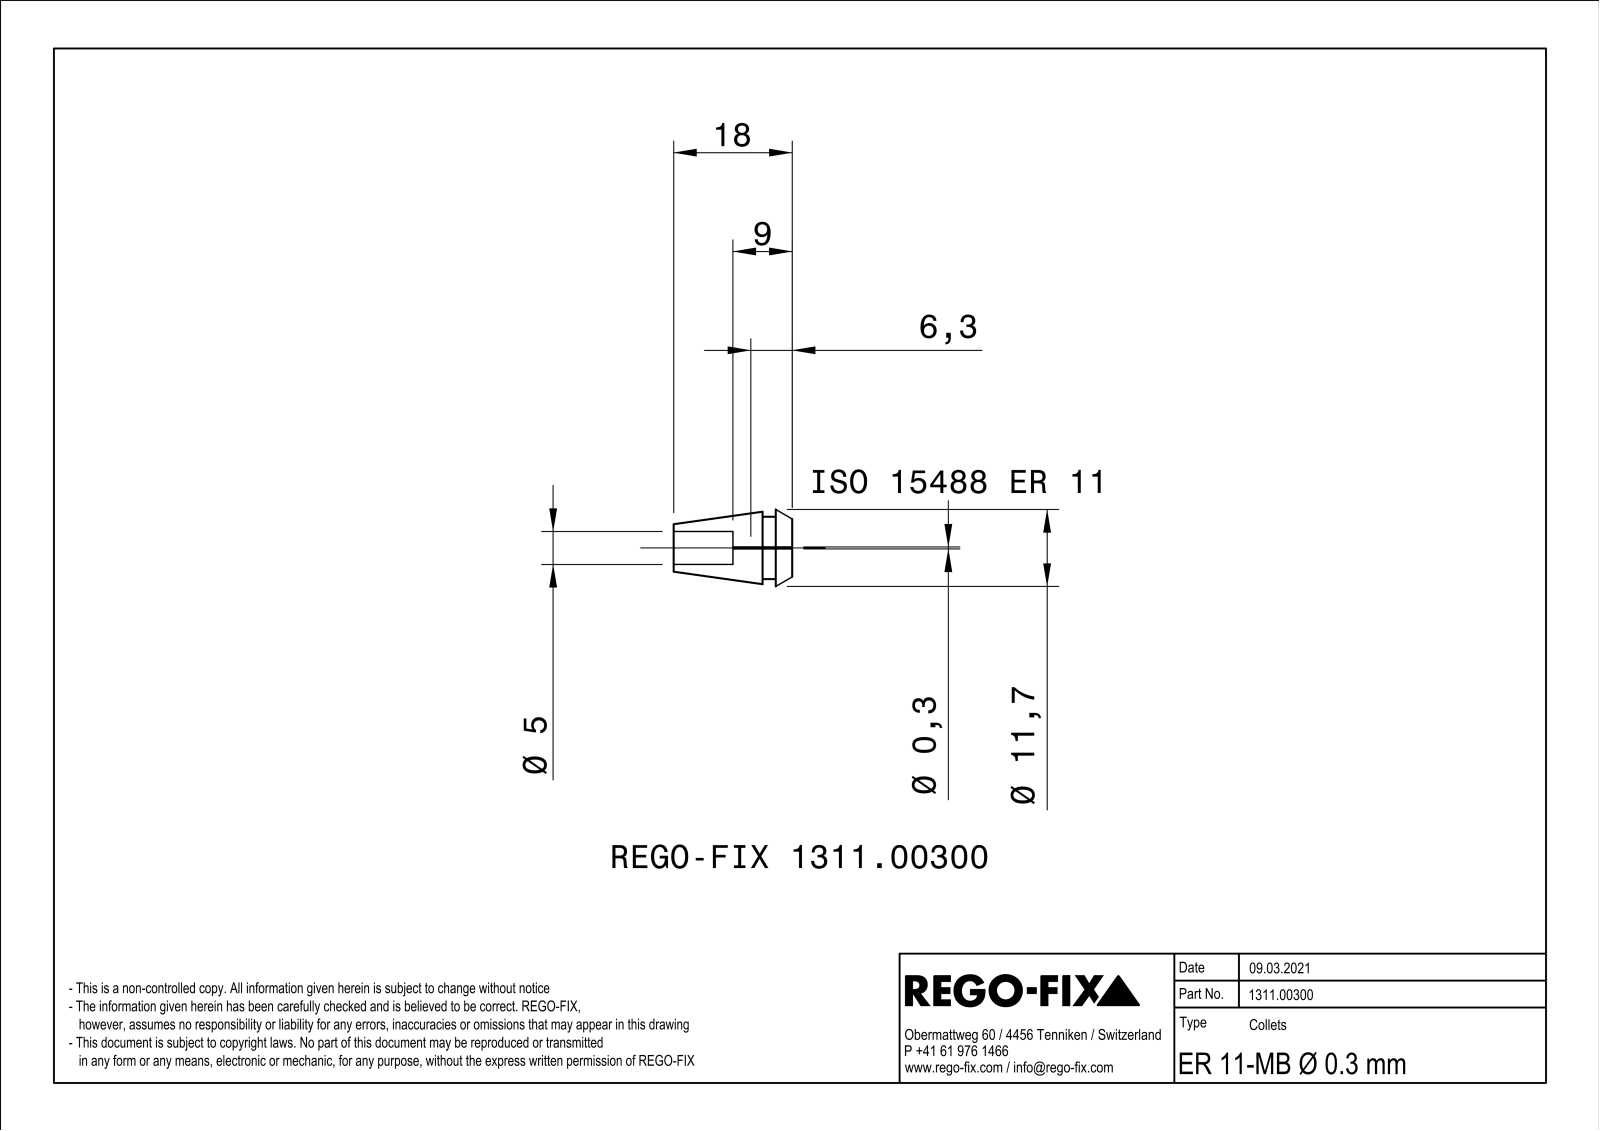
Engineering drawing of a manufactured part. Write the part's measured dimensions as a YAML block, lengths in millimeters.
part_name: "NOCUT"
step_written_by: "SIEMENS PLM Software Solid Edge ST10 (AUTOMOTIVE_DESIGN)"
units: millimeters
bodies: {solids: 1, faces: 91, planar: 26, cylindrical: 19, other: 46}
overall_size: [18, 11.15, 11.13]
volume: 902
surface_area: 1210
round_holes:
  - {diameter: 1.5, count: 3}
  - {diameter: 5, count: 1}
round_bosses_or_shafts:
  - {diameter: 9.5, count: 1}
partial_cylinders:
  - {radius: 25, count: 3}
  - {radius: 0.15, count: 1}
face_to_face_distances: [0.8, 0.34, 0.46, 4.5, 9, 2.5, 18, 15.5, 2, 13.5]
hole_center_spacings: [1.7, 2.94]
